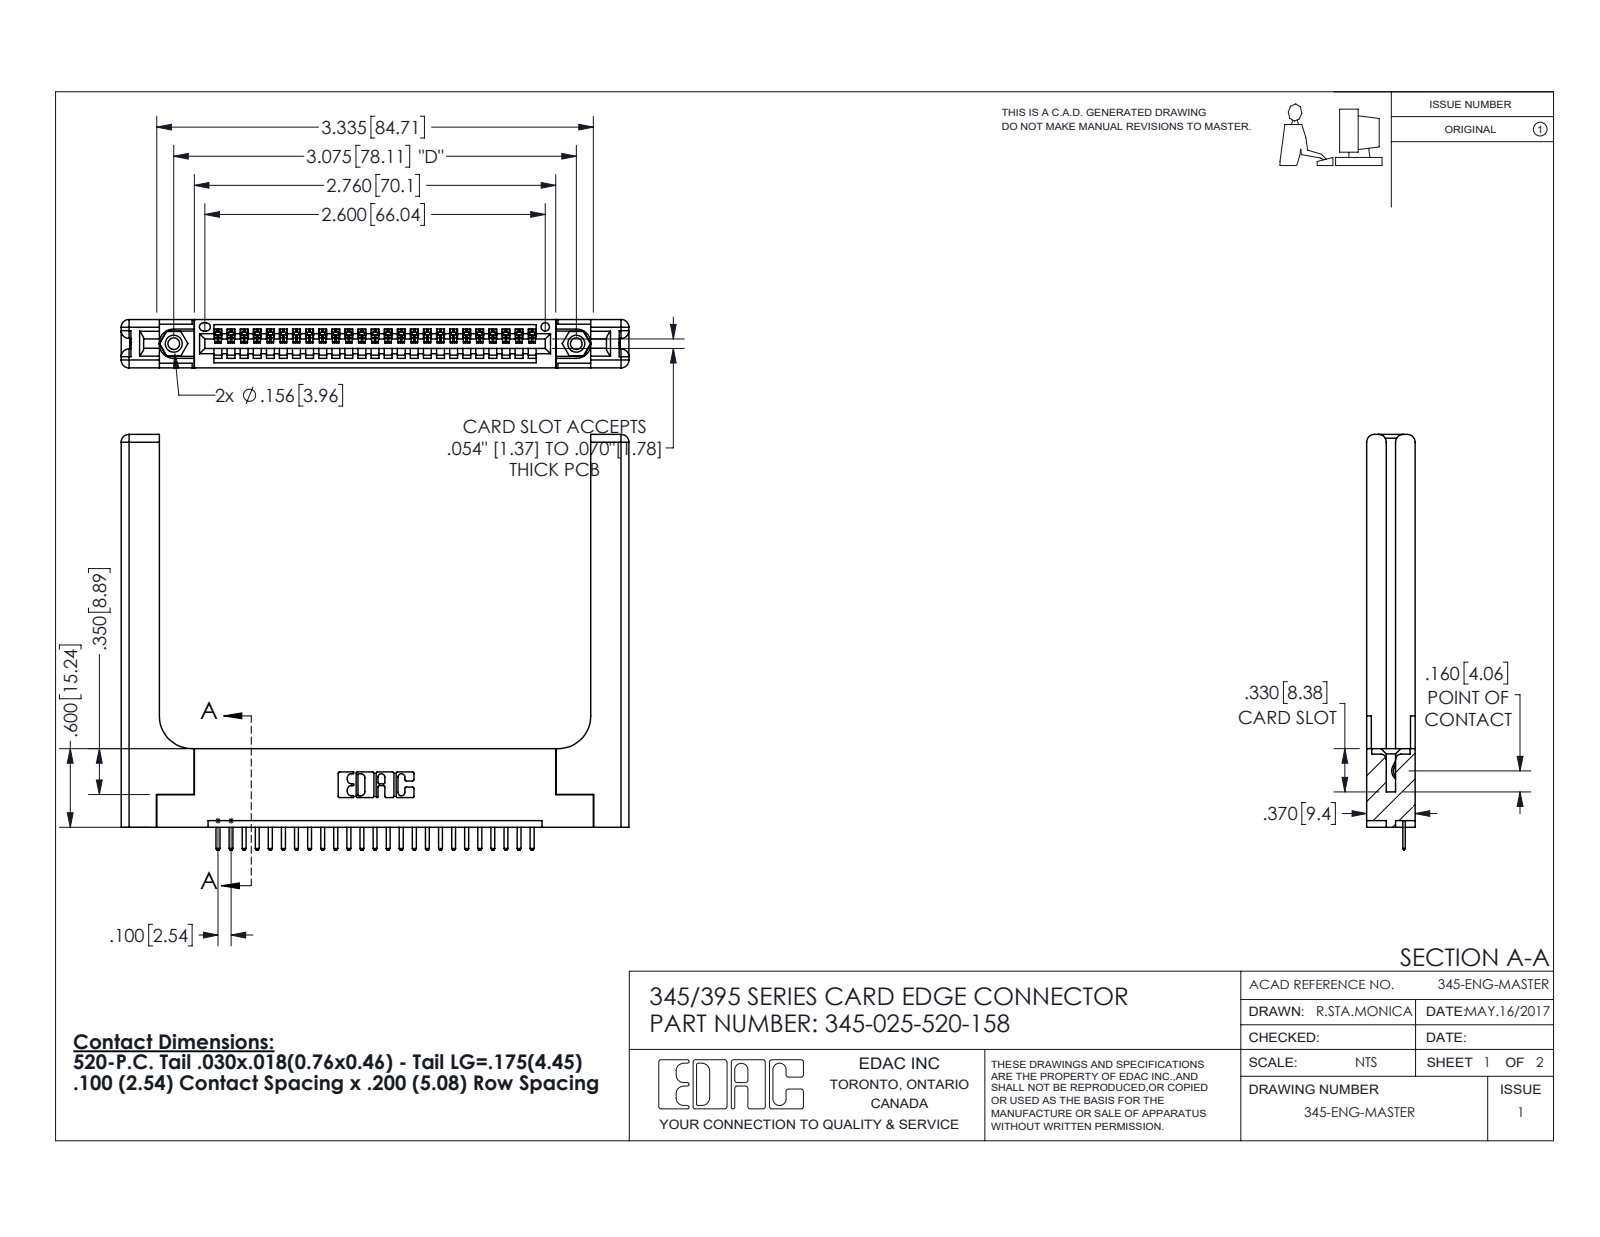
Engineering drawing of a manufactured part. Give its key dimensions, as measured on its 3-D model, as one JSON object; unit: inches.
{"part_name": "345-220-058_345-220-058; 345 Part_Flush Mounting Lugs - 0.156 Dia-TH; 345-025-520-158; 345-250-001_345-250-001-102 (+1 more)", "step_written_by": "SolidWorks 2016 (CONFIG_CONTROL_DESIGN)", "units": "inches", "bodies": {"solids": 30, "faces": 1932, "planar": 1278, "cylindrical": 594, "other": 60}, "overall_size": [3.879, 3.175, 0.37], "volume_in3": 1.077, "surface_area_in2": 26.34, "round_holes": [[0.089, 2], [0.125, 2], [0.156, 2], [0.064, 1]], "round_bosses_or_shafts": [[0.155, 2]], "partial_cylinders_radius": [[0.01, 52], [0.006, 50], [0.01, 22], [0.06, 16], [0.007, 6], [0.031, 6], [0.026, 3], [0.03, 2]], "face_to_face_distances": [0.37, 0.072, 0.298, 0.2, 0.148, 0.15, 0.077, 0.22, 0.098, 0.272], "hole_center_spacings": [0.27, 2.84, 3.075]}
